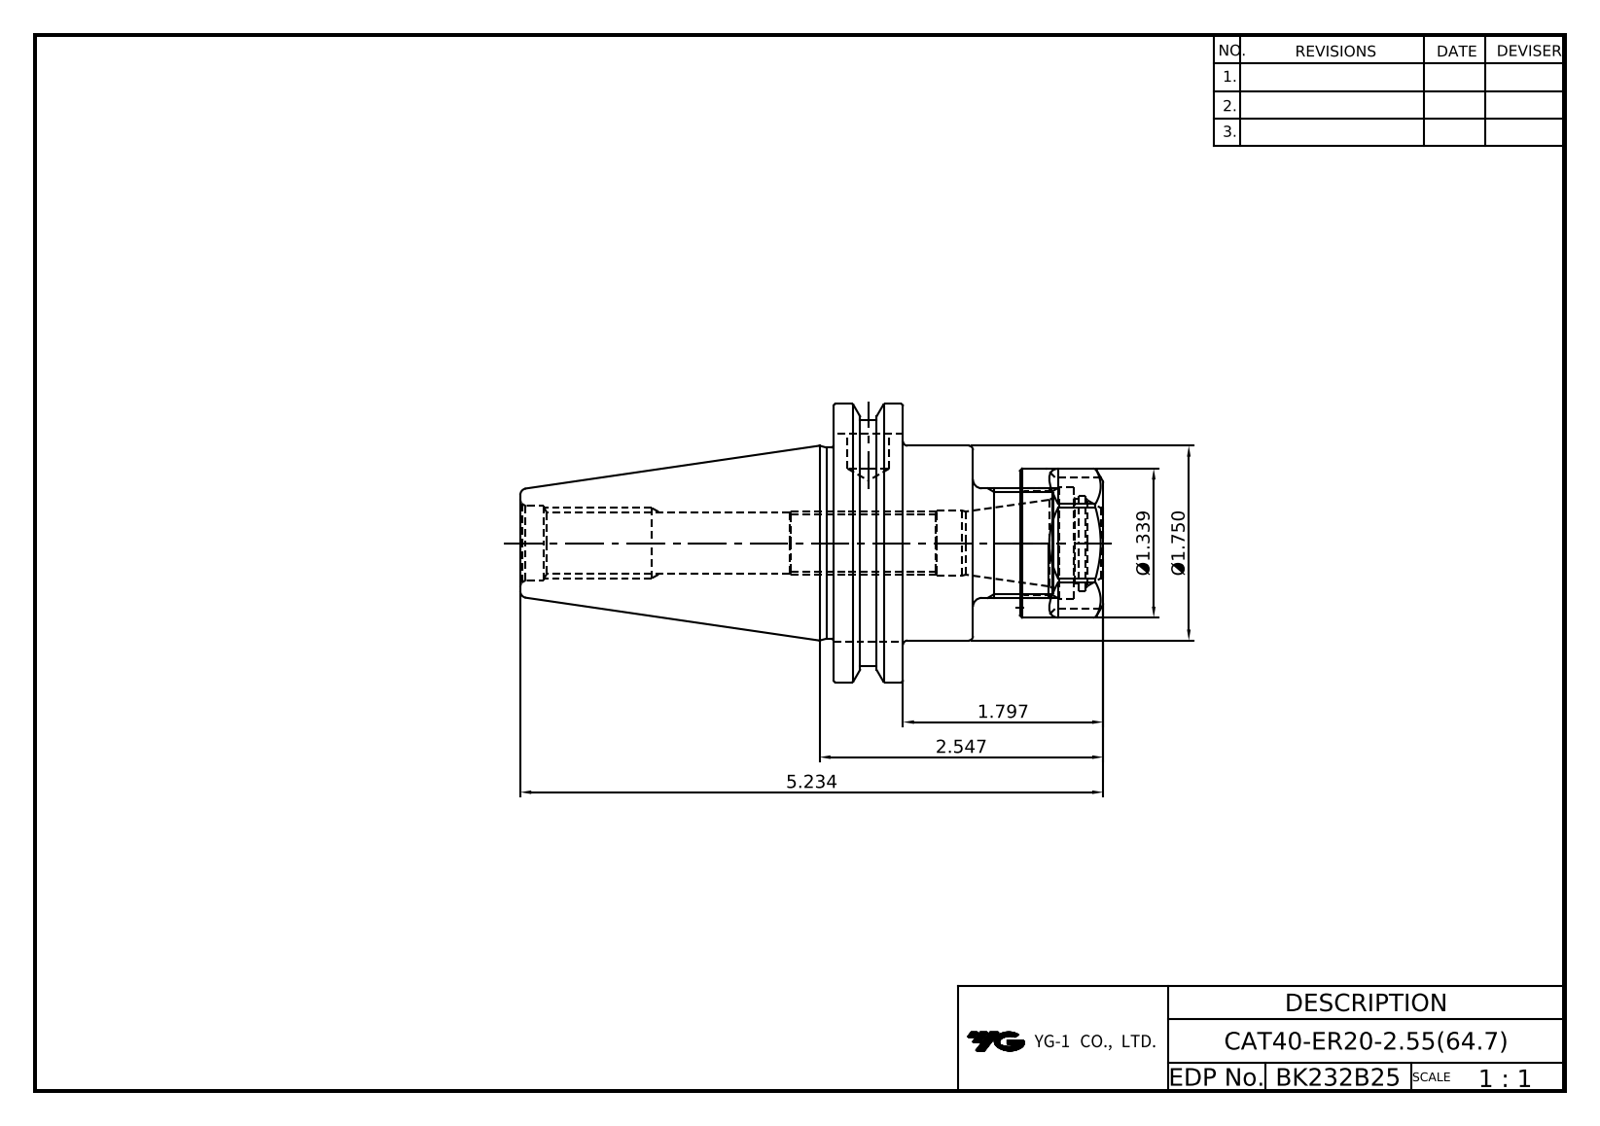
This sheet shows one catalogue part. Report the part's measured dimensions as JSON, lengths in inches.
{"part_name": "LO-CAT40-ER20-64.77; ER20NUT", "step_written_by": "Autodesk Inventor 2025 (AUTOMOTIVE_DESIGN)", "units": "inches", "bodies": {"solids": 2, "faces": 90, "planar": 48, "cylindrical": 21, "other": 21}, "overall_size": [5.237, 2.5, 2.405], "volume_in3": 8.335, "surface_area_in2": 47.64, "round_holes": [[0.375, 1], [0.495, 1], [0.527, 1], [0.587, 1], [0.63, 1], [0.642, 1], [0.724, 1], [0.857, 1], [0.925, 1], [1.004, 1]], "round_bosses_or_shafts": [[2.5, 1], [2.217, 1], [1.75, 1], [1.717, 1], [1.339, 1], [0.984, 1]], "face_to_face_distances": [0.625, 1.253, 0.628, 2.425, 1.8, 1.172, 0.748, 1.677, 1.052, 0.424]}
